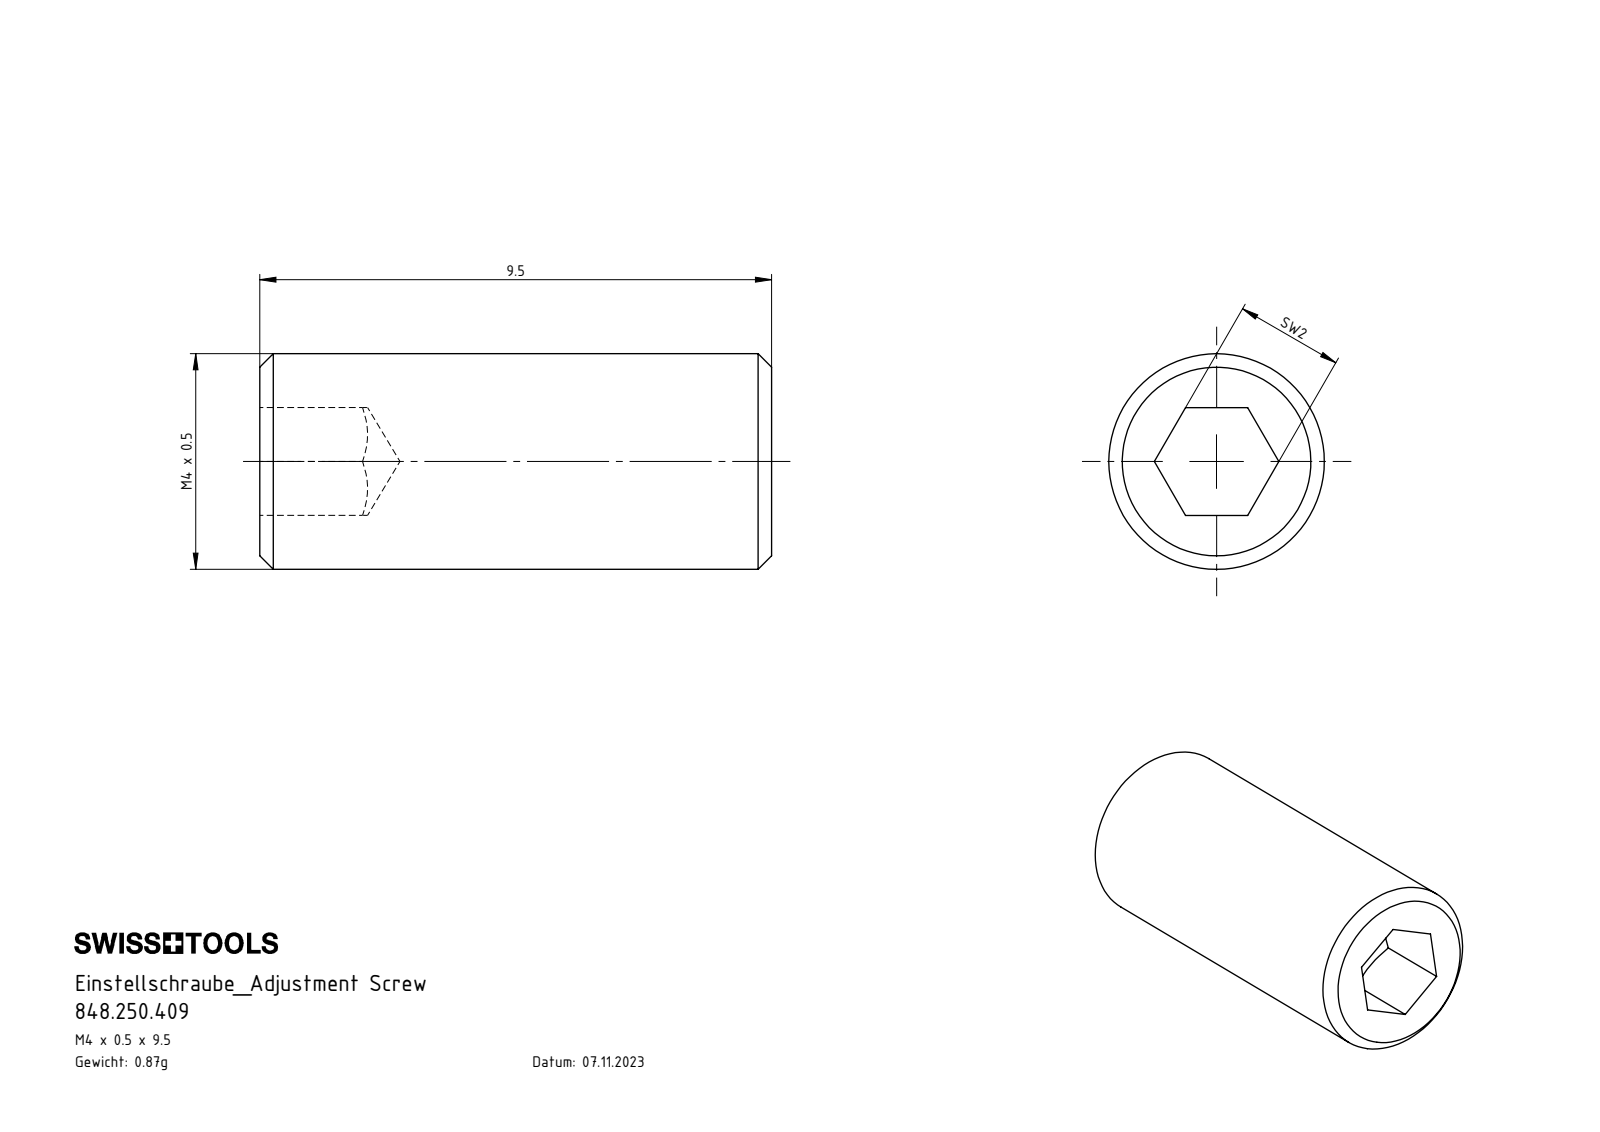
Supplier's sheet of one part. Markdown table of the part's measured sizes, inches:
| quantity | value |
| --- | --- |
| part name | 848.250.409 |
| STEP written by | SolidWorks 2022 (AUTOMOTIVE_DESIGN) |
| units | inches |
| bodies | 1 solid, 16 faces (8 planar, 2 cylindrical, 6 other) |
| overall size | 0.374 × 0.157 × 0.157 |
| volume | 0.007 in³ |
| surface area | 0.24 in² |
| round bosses / shafts (diameter × count) | 0.157 × 1 |
| main face-to-face distances | 0.079, 0.374 |
